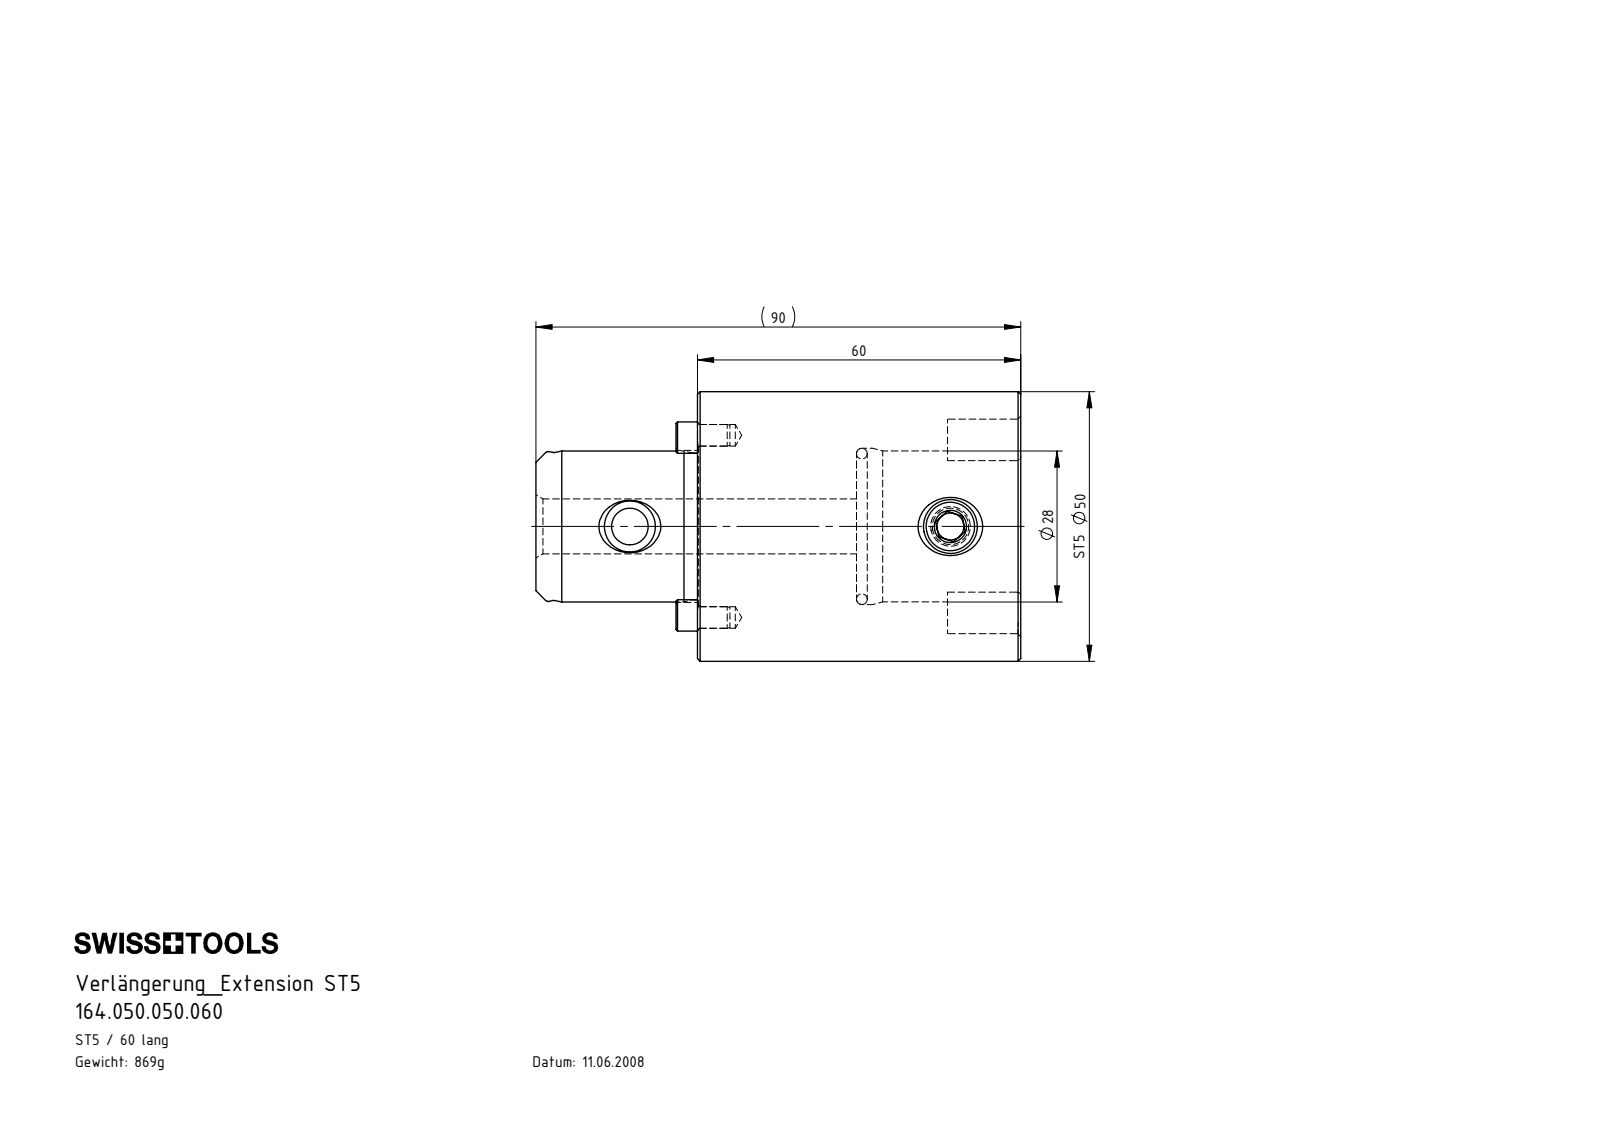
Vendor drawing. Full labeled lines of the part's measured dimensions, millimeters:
Part name (STEP PRODUCT): ST5-ER1.001.012_A; ST5-ST5.K01.060_A; DIN 3771 - 25x2; ST5-ER2.001.010_A (+1 more)
STEP written by: SolidWorks 2015 (CONFIG_CONTROL_DESIGN)
Units: millimetres
Bodies: 5 solids, 154 faces (26 planar, 43 cylindrical, 85 other)
Overall size (bounding box): 90 × 50 × 50
Volume: 110 958 mm³ · Surface area: 22 540 mm²
Round holes (diameter × count): ⌀4 ×2, ⌀6.8 ×1, ⌀9 ×1, ⌀10.2 ×1, ⌀28 ×1, ⌀29 ×1
Round bosses / shafts (diameter × count): ⌀50 ×1, ⌀27.8 ×1, ⌀27.3 ×1, ⌀10 ×1
Partial cylindrical surfaces — rounded edges, fillets, slot ends (radius × count): R0.5 ×4, R4.2 ×2, R4.47 ×2, R14.05 ×2
Main face-to-face distances: 60, 29.5, 30.5, 30, 59.5, 90, 24.1, 76.4, 46.4, 16.9
Hole centre spacings: 16.9, 33.8, 59.5
